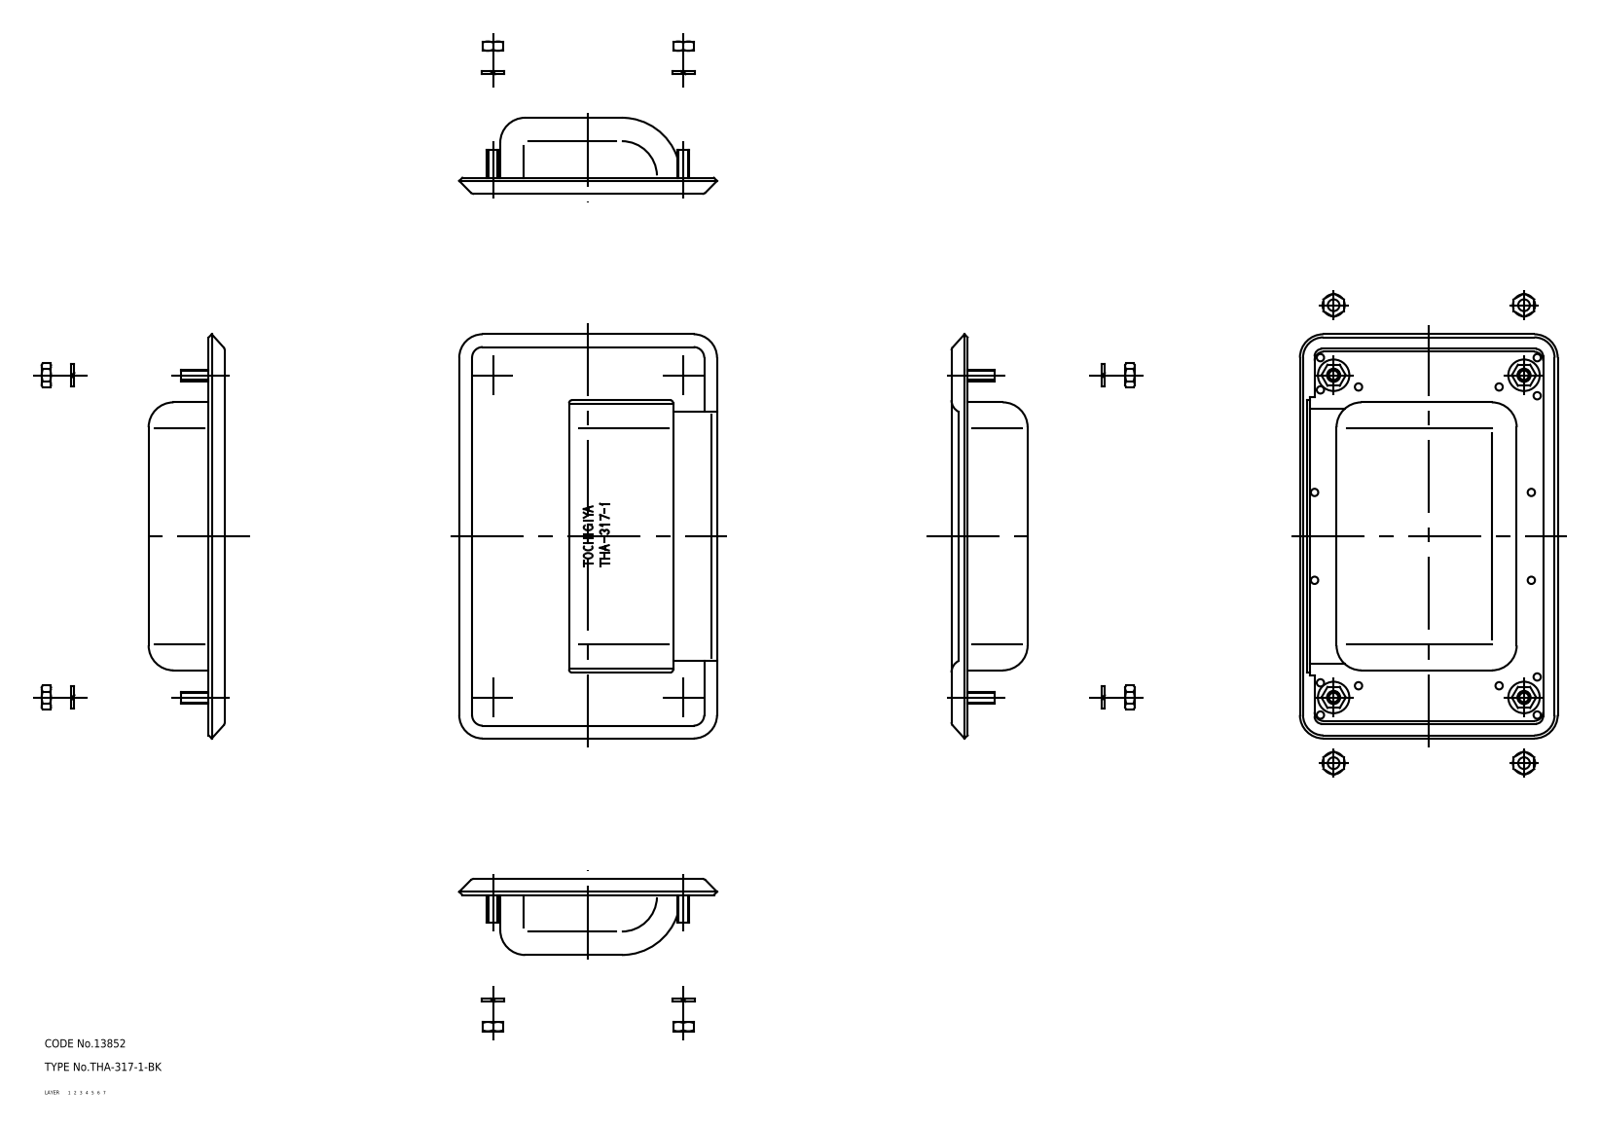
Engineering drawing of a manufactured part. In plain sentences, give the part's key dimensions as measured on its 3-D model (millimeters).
The part is named "PC3110-prt0; PC3110-prt1; PC3110-prt2; PC3110-prt3 (+7 more)". Its 3-D file was written by "spGate 20.6.3 (****-****-****-****) (AUTOMOTIVE_DESIGN)". It is 9 solids with 578 faces: 206 planar, 174 cylindrical and 198 other. Overall it measures 138 by 88 by 26 millimeters. Its volume is 8 231 cubic millimeters and its surface area 55 173 square millimeters. Round holes: 16 of diameter 2.5, 4 of diameter 4. Round bosses or shafts: 4 of diameter 7.6. Partial cylindrical surfaces (rounded edges, fillets, slot ends): 44 of radius 0.5, 8 of radius 3, 8 of radius 6, 8 of radius 8, 7 of radius 8.5, 7 of radius 10, 5 of radius 1.5, 3 of radius 1. The main face-to-face distances are 1.06, 0.5, 24.44, 1.56, 25.5, 26, 24.94, 23.94, 1, 2.5. The hole center spacings are 7.5, 9.39, 16.4, 46.04, 56.64, 61.81, 69.76, 74.
